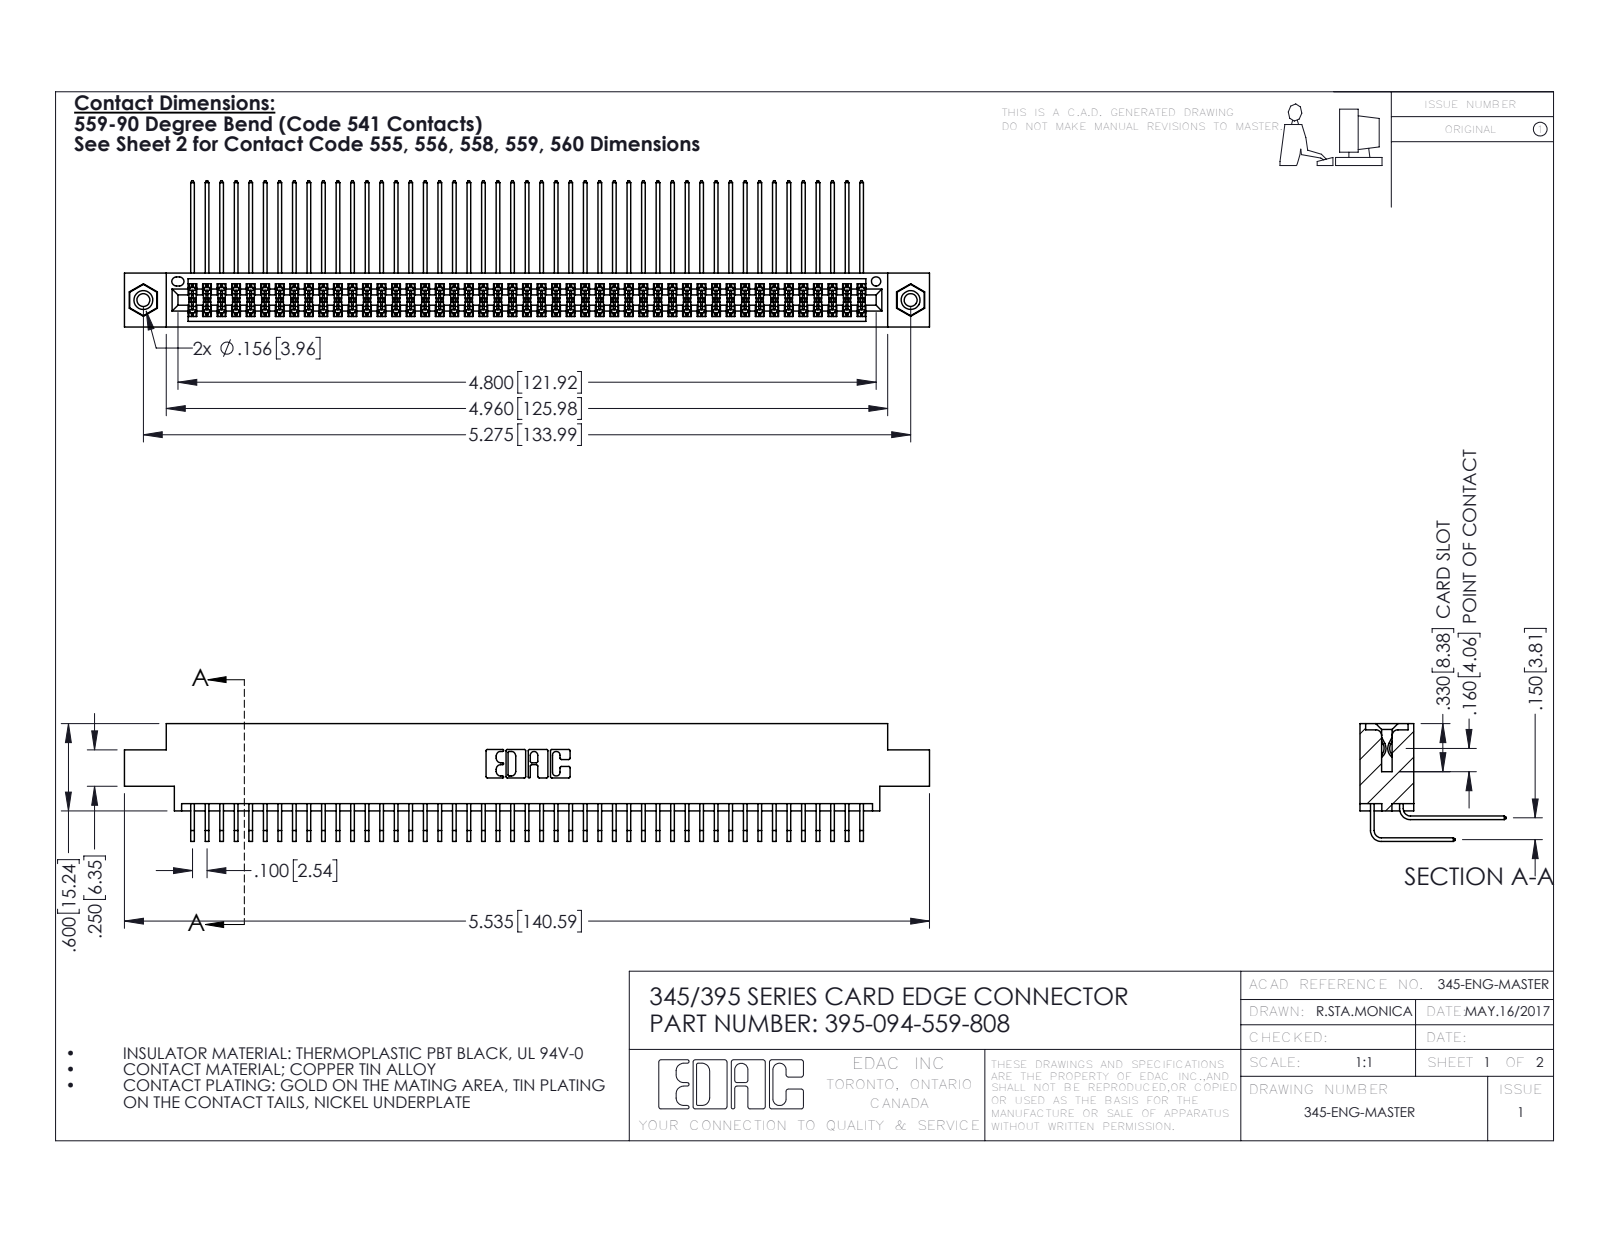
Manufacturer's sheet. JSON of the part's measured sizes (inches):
{"part_name": "395-094-559-808; 345-292-001_559 Tail - 2; 345 Part_0.170 Offset - 0.156 Dia-TI; 345-292-001_558 559 Tail - 1 (+1 more)", "step_written_by": "SolidWorks 2016 (CONFIG_CONTROL_DESIGN)", "units": "inches", "bodies": {"solids": 97, "faces": 5078, "planar": 3406, "cylindrical": 1656, "other": 16}, "overall_size": [5.535, 1.005, 0.809], "volume_in3": 0.862, "surface_area_in2": 36.71, "round_holes": [[0.089, 2], [0.125, 2], [0.156, 2], [0.064, 1]], "round_bosses_or_shafts": [[0.155, 2]], "partial_cylinders_radius": [[0.006, 141], [0.01, 22], [0.007, 6], [0.031, 6], [0.026, 3], [0.014, 2], [0.019, 2], [0.022, 2]], "face_to_face_distances": [0.072, 0.298, 0.37, 0.2, 0.098, 0.272, 0.025, 0.225, 0.175, 0.15], "hole_center_spacings": [0.27, 5.039, 5.275]}
